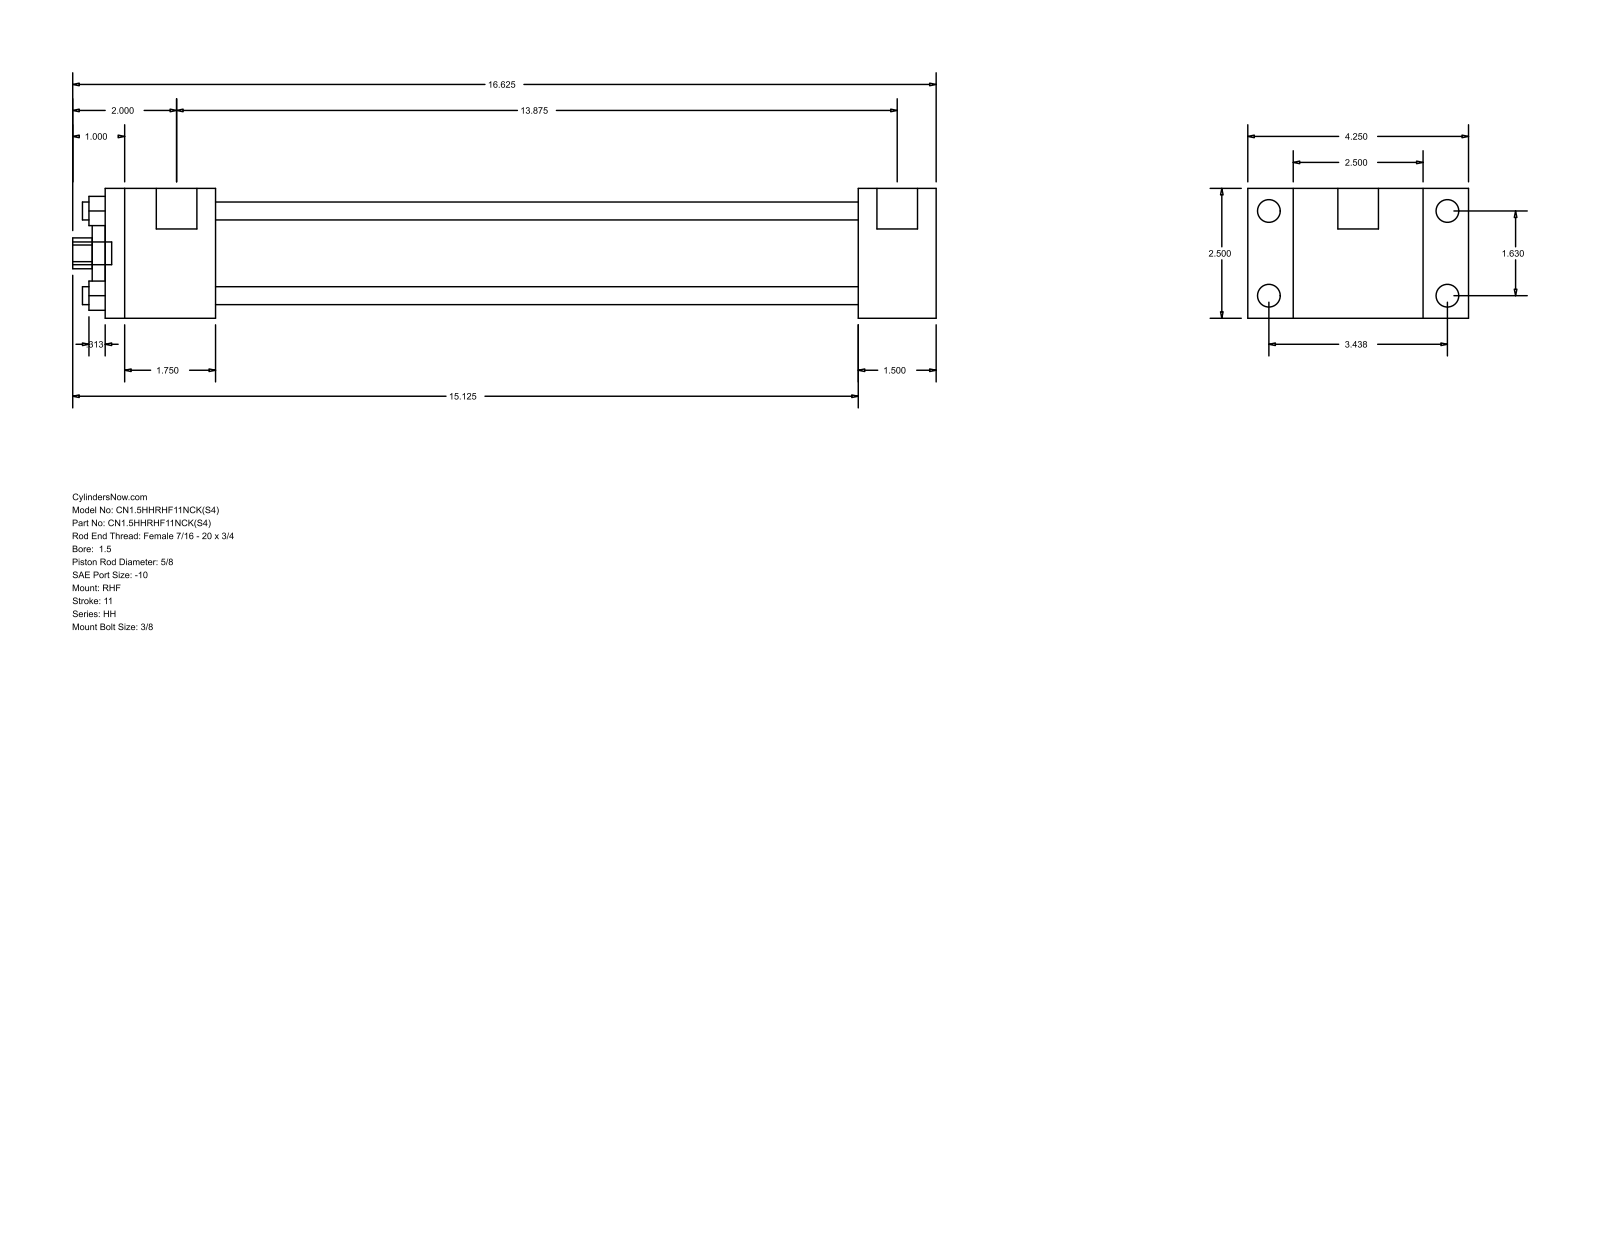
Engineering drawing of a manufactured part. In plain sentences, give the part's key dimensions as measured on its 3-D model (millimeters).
The part is named "HH_RHF__0150_0.625". Its 3-D file was written by "GSSL Pune (CONFIG_CONTROL_DESIGN)". It is 0 solids with 88 faces: 60 planar, 28 cylindrical and 0 other. Overall it measures 422.27 by 107.95 by 63.5 millimeters. Round holes: 4 of diameter 8.76, 1 of diameter 15.88, 1 of diameter 28.57, 1 of diameter 44.45. Round bosses or shafts: 4 of diameter 11.13, 4 of diameter 5.56, 2 of diameter 19.84, 1 of diameter 11.11. Partial cylindrical surfaces (rounded edges, fillets, slot ends): 1 of radius 7.54. The main face-to-face distances are 63.5, 22.23, 85.73, 38.09, 368.3, 406.39, 107.96, 53.97, 314.33, 352.42. The hole center spacings are 29.27, 41.4, 58.55.
